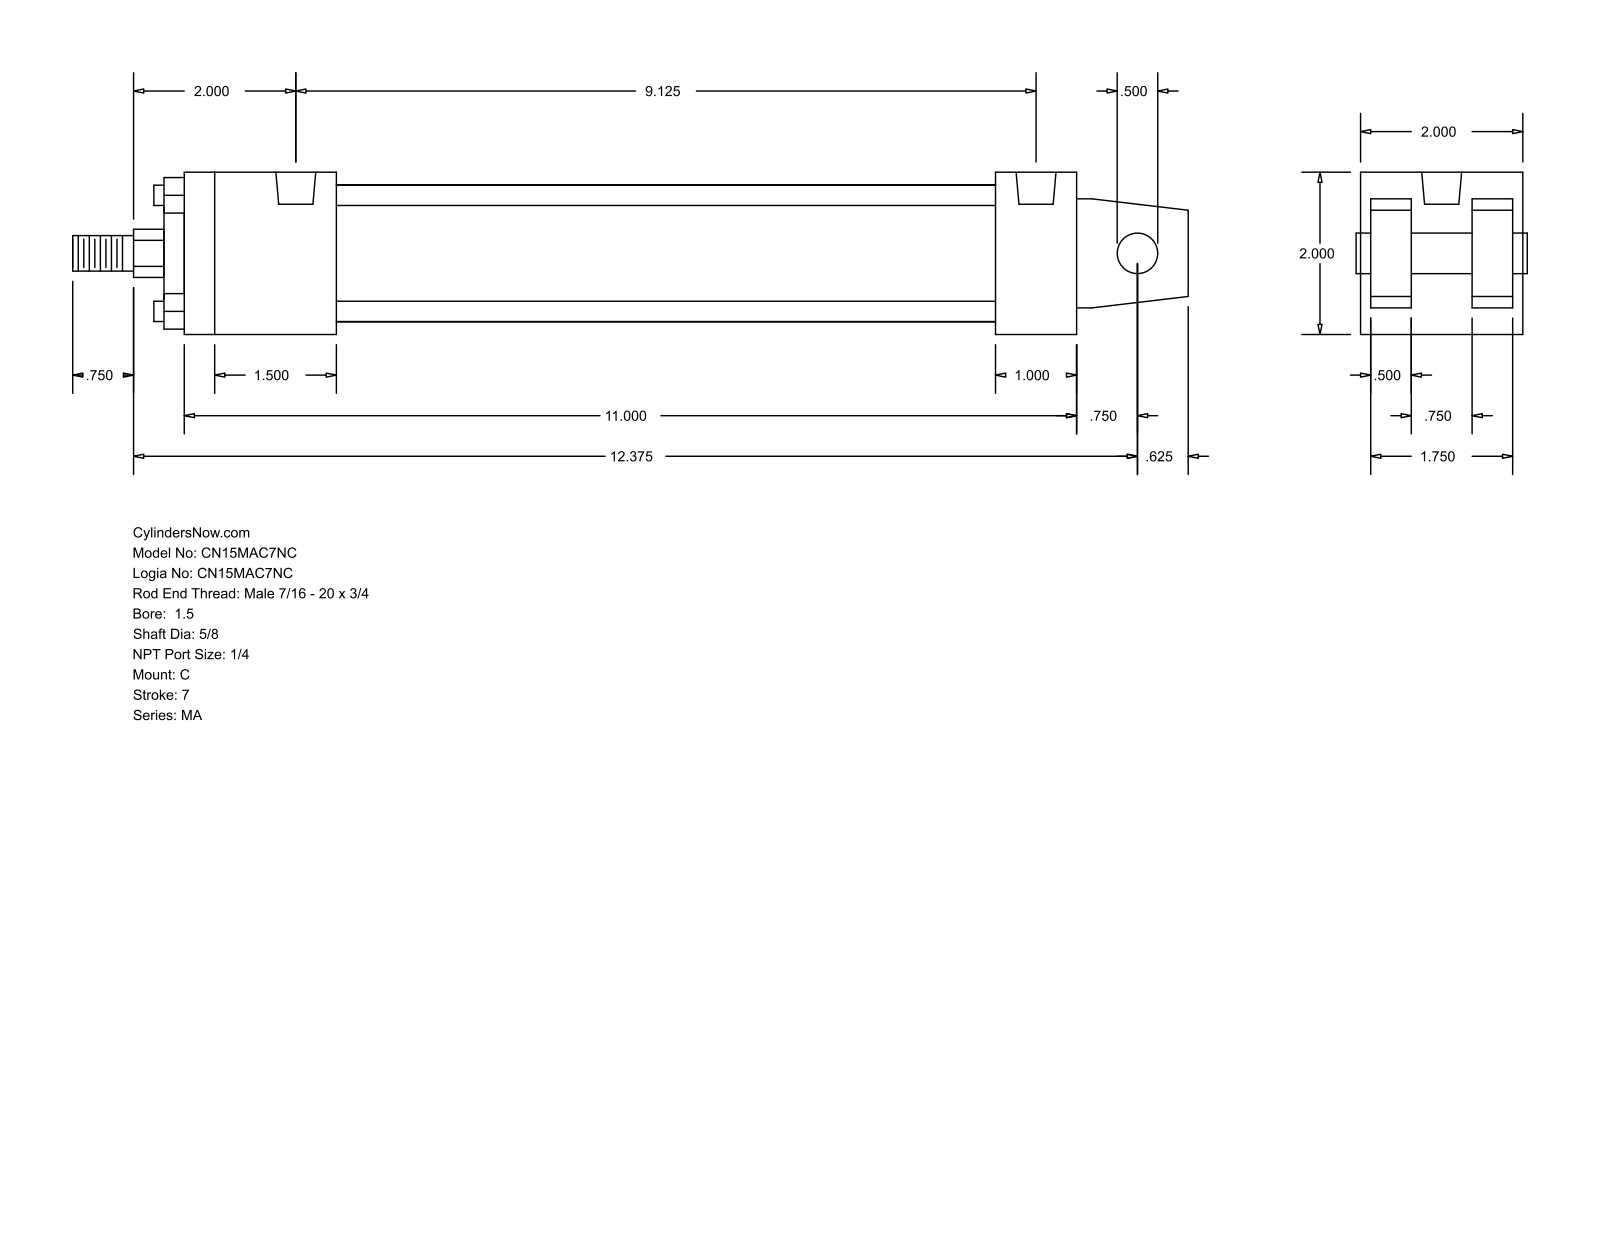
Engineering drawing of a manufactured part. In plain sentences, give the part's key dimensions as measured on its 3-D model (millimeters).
The part is named "MA_C__0150_0.625". Its 3-D file was written by "GSSL Pune (CONFIG_CONTROL_DESIGN)". It is 0 solids with 103 faces: 76 planar, 27 cylindrical and 0 other. Overall it measures 349.25 by 50.8 by 50.8 millimeters. Round holes: 4 of diameter 7.94, 2 of diameter 12.49. Round bosses or shafts: 4 of diameter 6.35, 1 of diameter 42.93, 1 of diameter 28.57, 1 of diameter 15.88, 1 of diameter 12.7, 1 of diameter 11.11. Partial cylindrical surfaces (rounded edges, fillets, slot ends): 1 of radius 7.54. The main face-to-face distances are 50.8, 34.93, 12.7, 15.87, 3.17, 47.63, 31.76, 279.39, 254, 25.39. The hole center spacings are 231.77.
